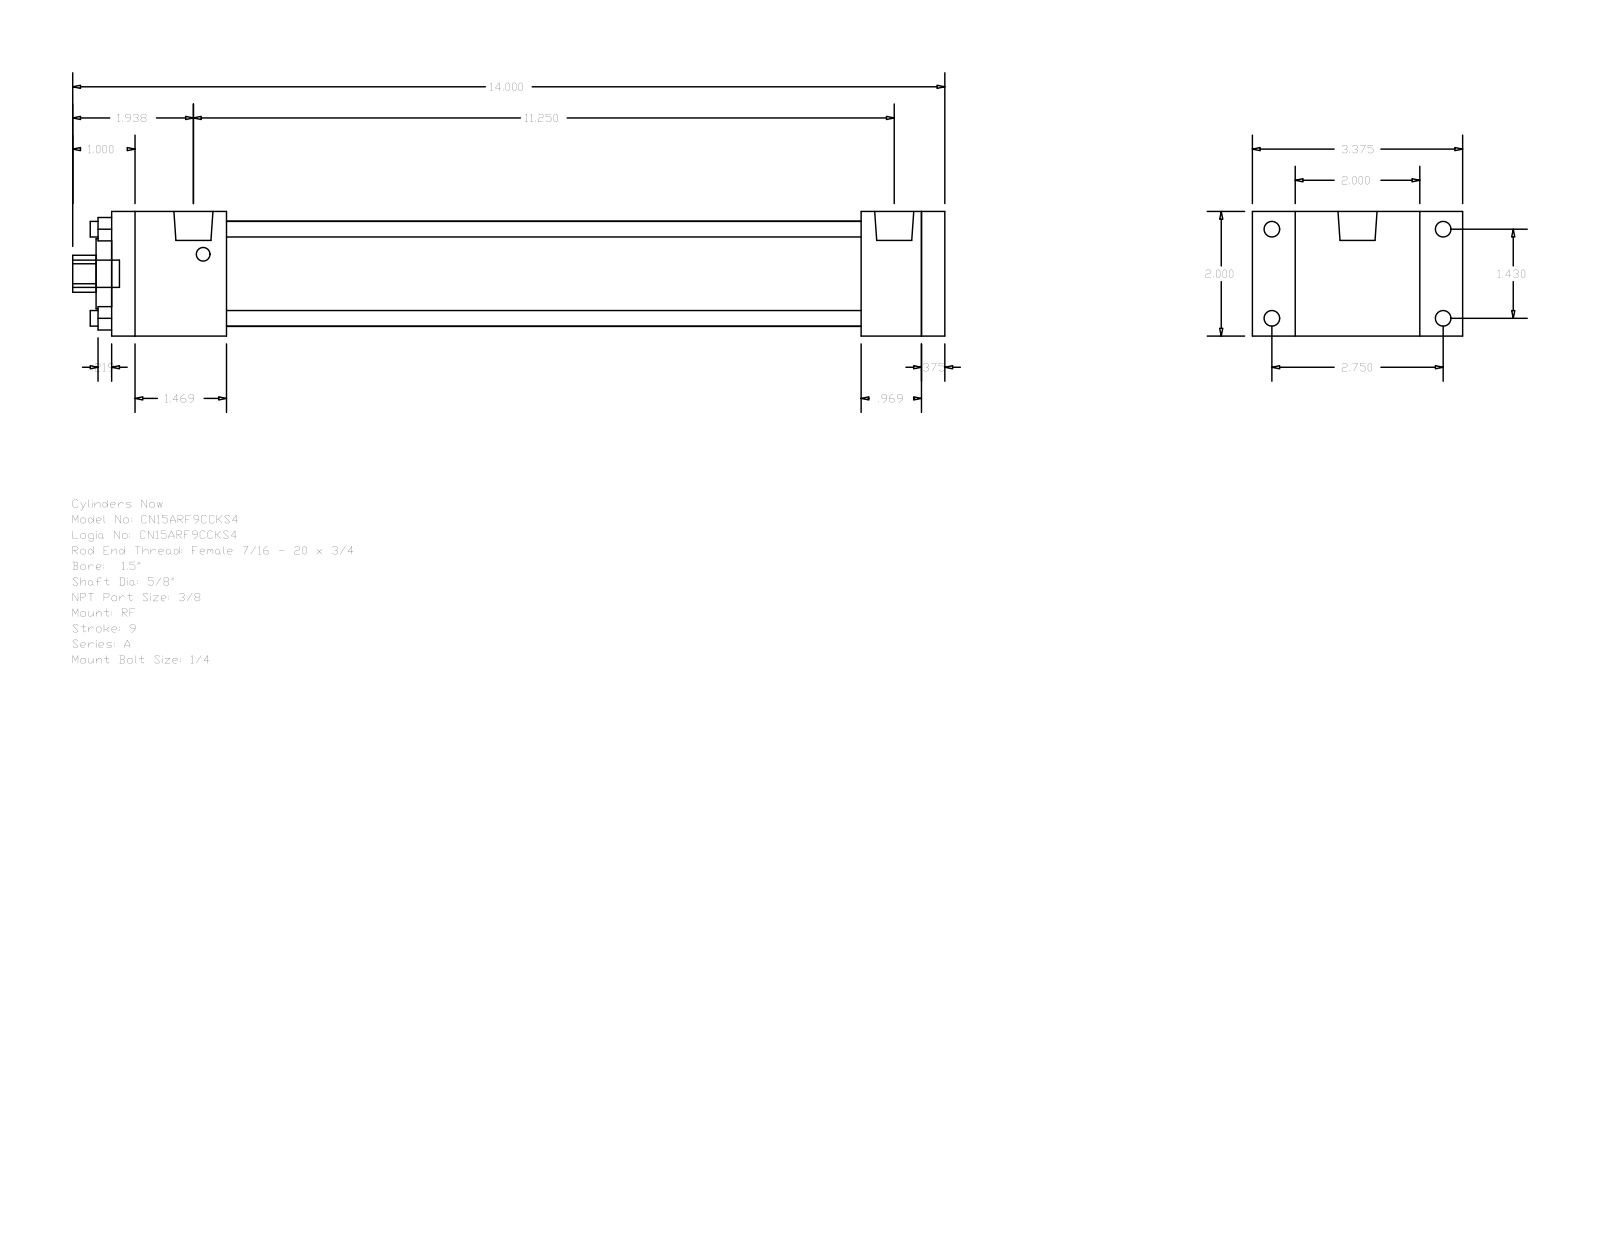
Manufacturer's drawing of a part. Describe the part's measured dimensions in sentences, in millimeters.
The part is named "A_RF__0150_0.625". Its 3-D file was written by "GSSL Pune (CONFIG_CONTROL_DESIGN)". It is 0 solids with 92 faces: 64 planar, 28 cylindrical and 0 other. Overall it measures 355.6 by 85.72 by 50.8 millimeters. Round holes: 4 of diameter 6.35, 1 of diameter 15.88, 1 of diameter 28.57, 1 of diameter 42.93. Round bosses or shafts: 4 of diameter 6.35, 4 of diameter 5.56, 2 of diameter 15.93, 1 of diameter 11.11. Partial cylindrical surfaces (rounded edges, fillets, slot ends): 1 of radius 7.54. The main face-to-face distances are 50.8, 9.53, 339.72, 330.19, 305.59, 24.6, 34.13, 46.83, 258.76, 283.36. The hole center spacings are 25.68, 36.32, 51.36.
